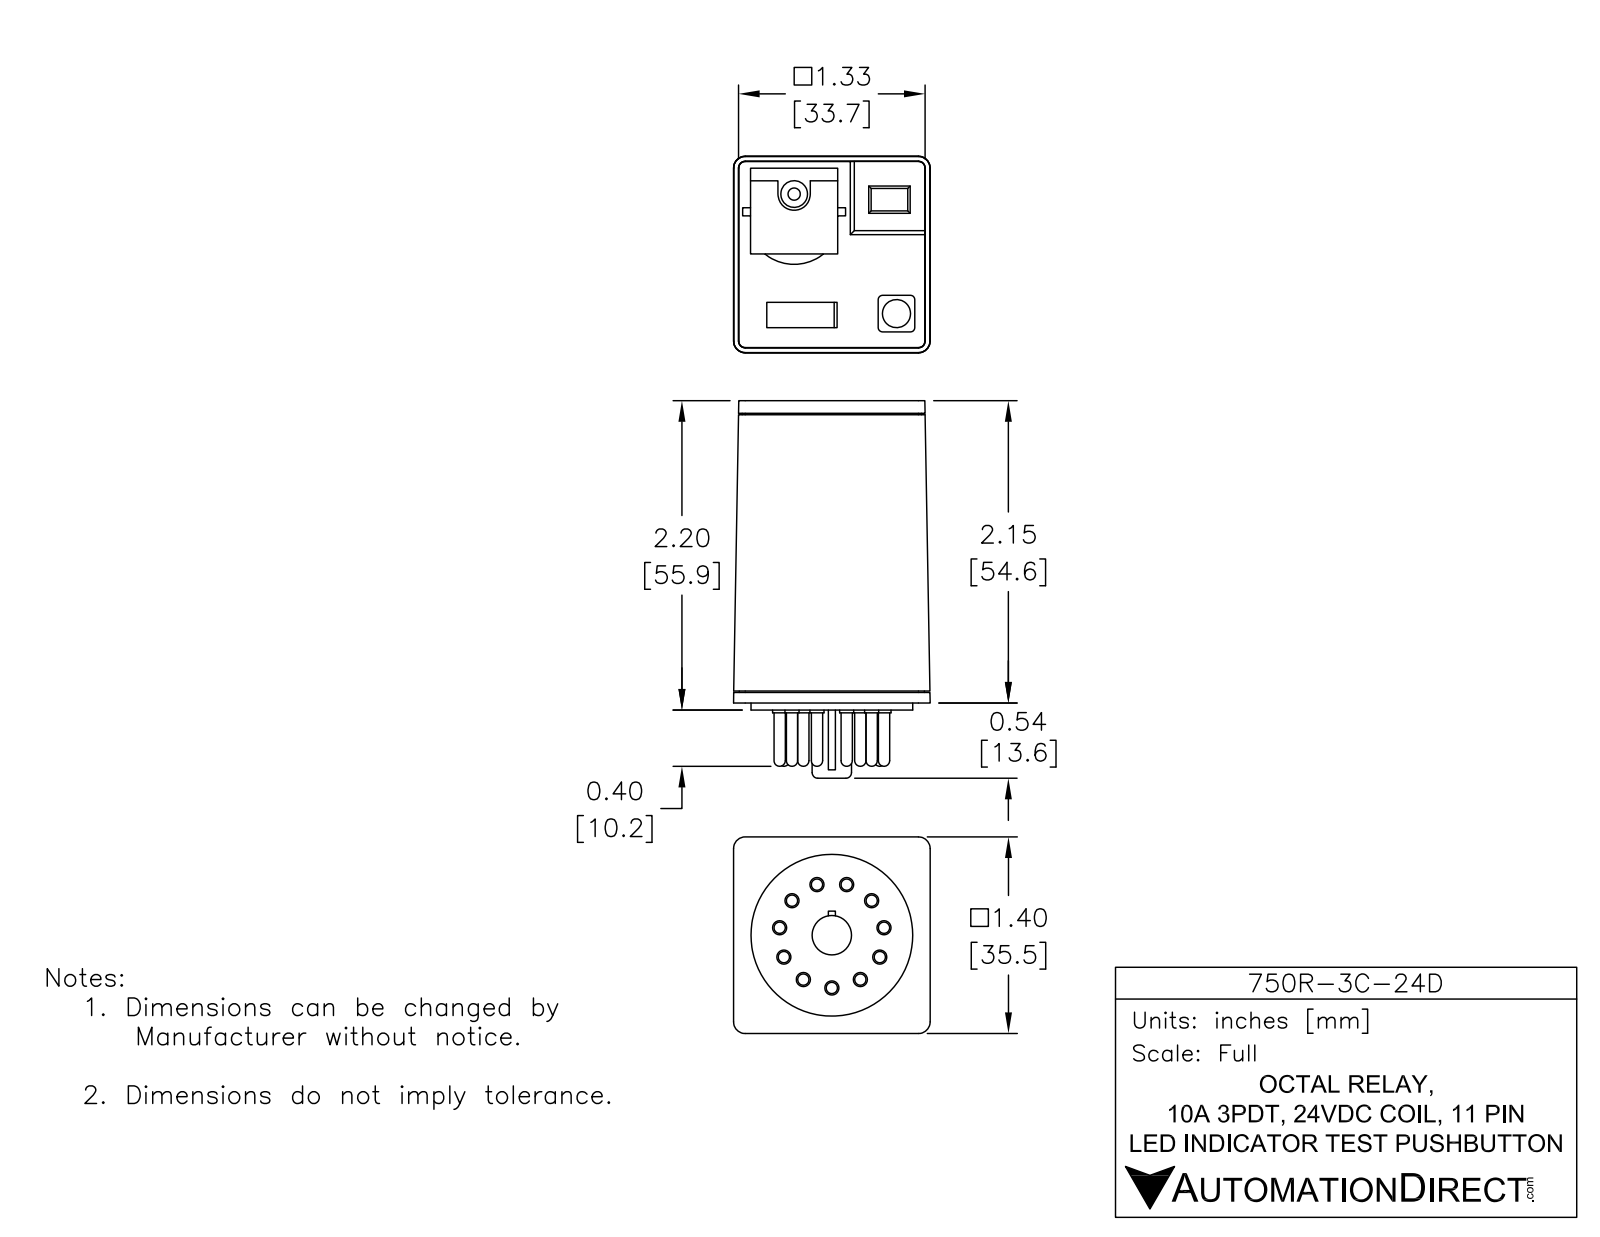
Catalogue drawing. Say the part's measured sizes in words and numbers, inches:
The part is named "750R-3C-24D". Its 3-D file was written by "SolidWorks 2014 (AUTOMOTIVE_DESIGN)". It is 1 solid with 180 faces: 93 planar, 62 cylindrical and 25 other. Overall it measures 2.685 by 1.398 by 1.398 inches. Its volume is 4.056 cubic inches and its surface area 17.68 square inches. Round holes: 1 of diameter 0.087, 1 of diameter 0.2. Round bosses or shafts: 11 of diameter 0.1, 11 of diameter 0.08, 1 of diameter 1.15, 1 of diameter 0.28, 1 of diameter 0.19. Partial cylindrical surfaces (rounded edges, fillets, slot ends): 4 of radius 0.03, 1 of radius 0.115, 1 of radius 0.33. The main face-to-face distances are 0.05, 2.15, 2.2, 2.11, 0.04, 2.19, 2.14, 0.085, 0.03, 2.16. The hole center spacings are 1.119.
